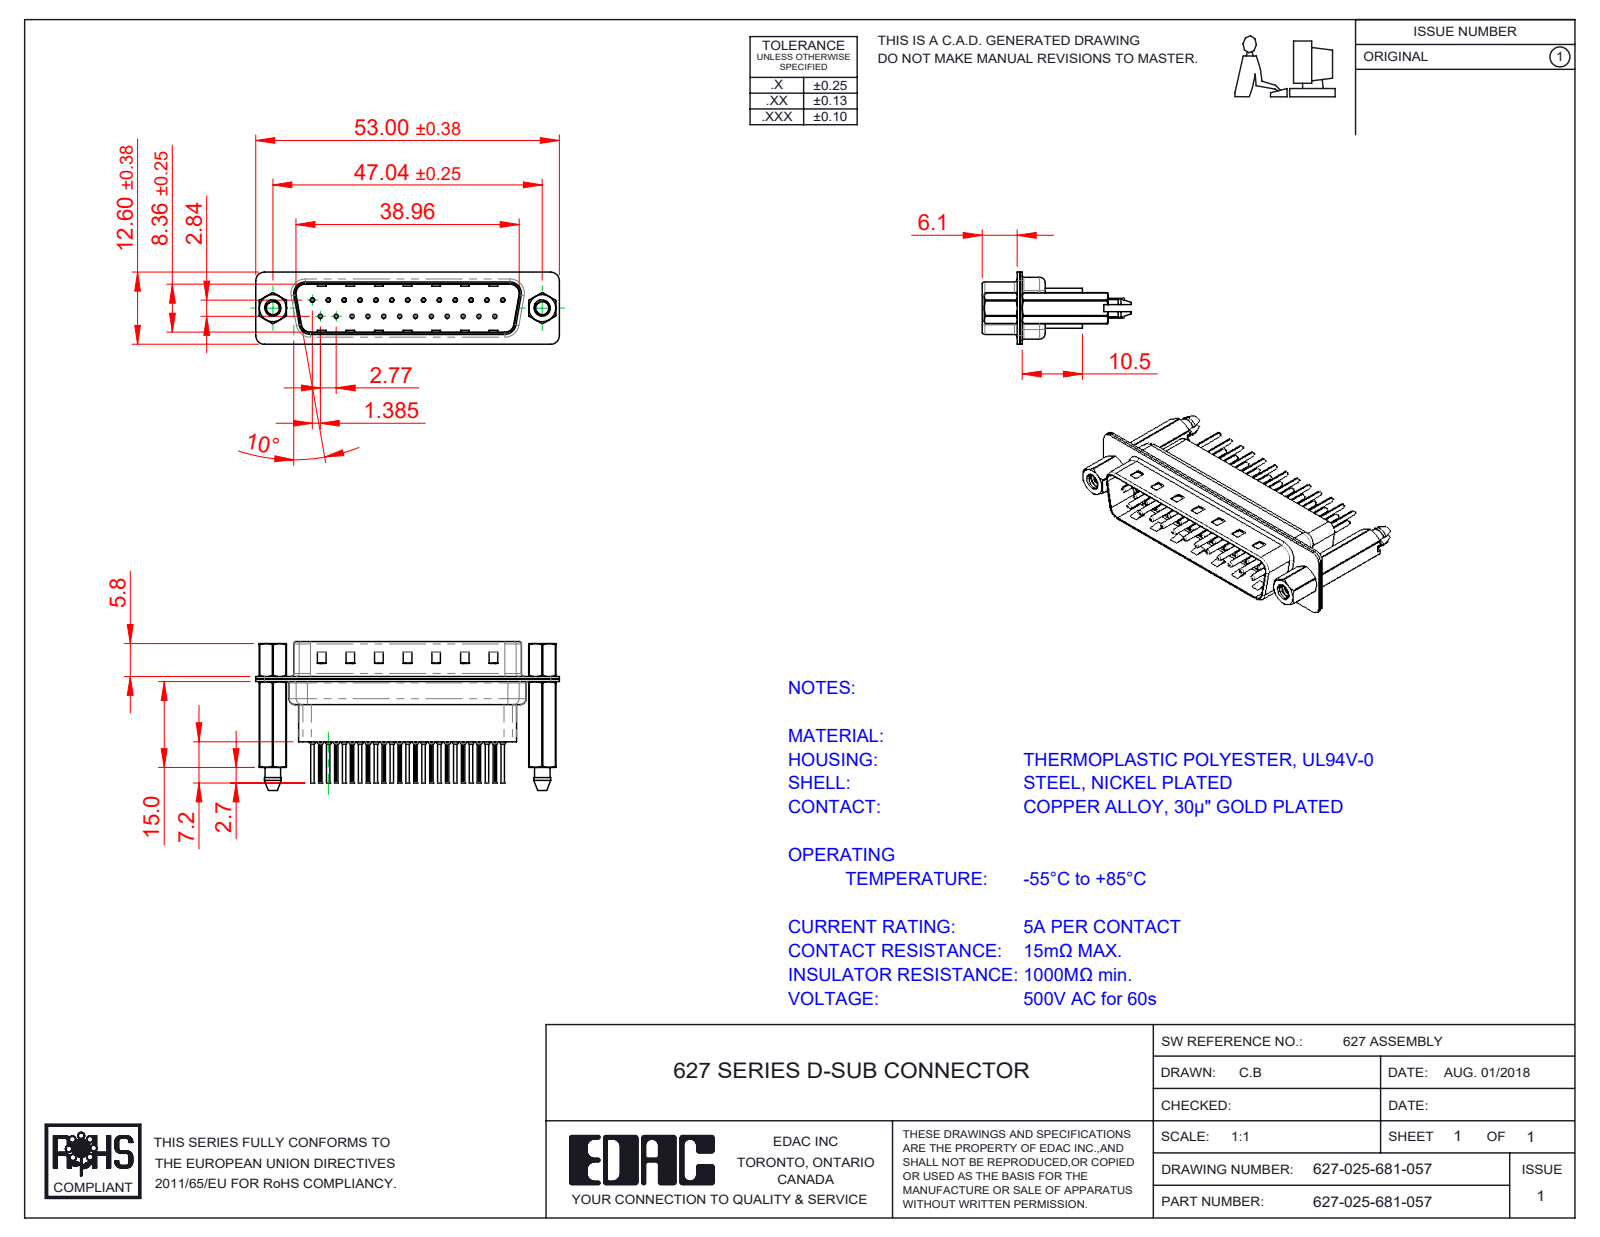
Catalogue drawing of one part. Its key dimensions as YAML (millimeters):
part_name: "627 Housing_25 HP; 627 Contact Row 2_61; 627 4-40 Threaded Boardlock_HP81; 627-025-681-057 (+4 more)"
step_written_by: "SolidWorks 2020 (CONFIG_CONTROL_DESIGN)"
units: millimeters
bodies: {solids: 32, faces: 3060, planar: 825, cylindrical: 1200, other: 1035}
overall_size: [53, 25.9, 12.6]
volume: 4417
surface_area: 11314
round_holes:
  - {diameter: 0.2, count: 25}
  - {diameter: 0.35, count: 25}
  - {diameter: 1.1, count: 25}
  - {diameter: 1.6, count: 25}
  - {diameter: 2.26, count: 2}
  - {diameter: 2.29, count: 2}
  - {diameter: 4, count: 2}
  - {diameter: 4.8, count: 2}
round_bosses_or_shafts:
  - {diameter: 2, count: 25}
  - {diameter: 1.5, count: 25}
  - {diameter: 0.75, count: 25}
  - {diameter: 0.6, count: 25}
  - {diameter: 4.9, count: 2}
  - {diameter: 2.79, count: 2}
partial_cylinders:
  - {radius: 0.1, count: 50}
  - {radius: 1.5, count: 18}
  - {radius: 2, count: 12}
  - {radius: 1.6, count: 10}
  - {radius: 0.5, count: 8}
  - {radius: 0.25, count: 4}
  - {radius: 0.6, count: 4}
  - {radius: 0.65, count: 4}
face_to_face_distances: [0.4, 0.45, 0.82, 9.58, 0.68, 7.68, 1.5, 0.9, 1.08, 8.08]
hole_center_spacings: [3.16, 8.31, 2.77, 5.54, 11.08, 16.62, 5.03, 5.04]
